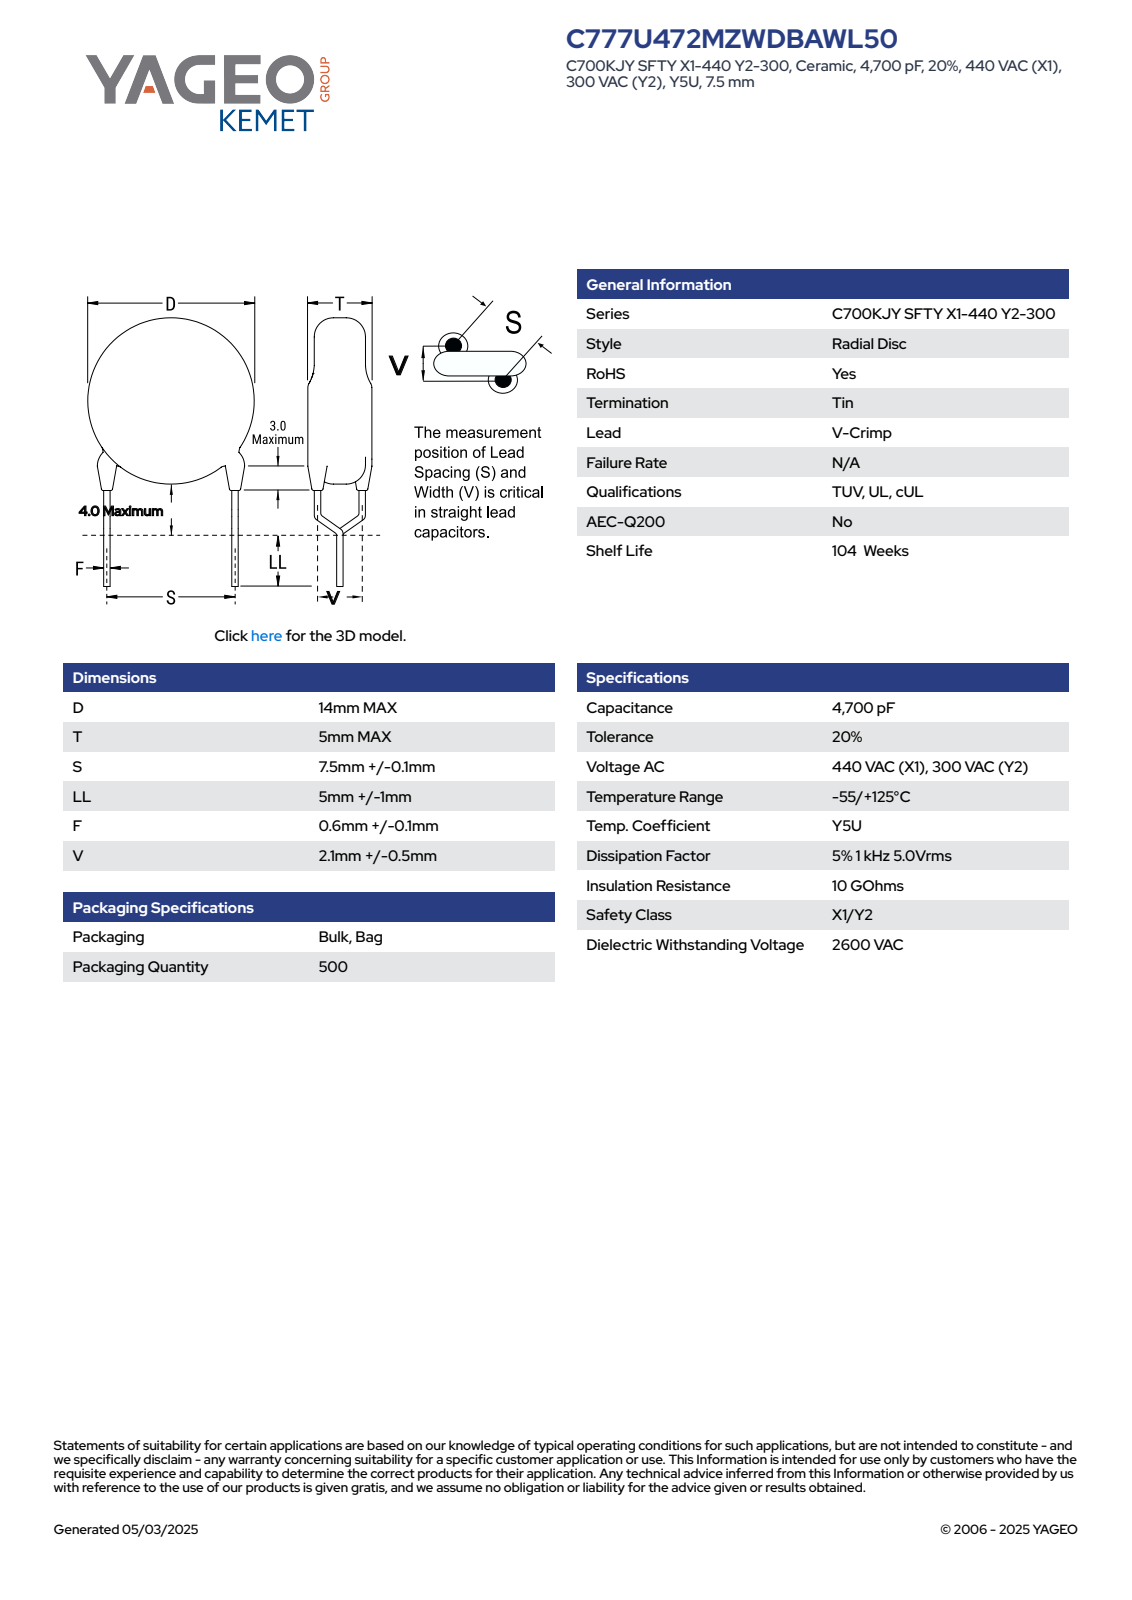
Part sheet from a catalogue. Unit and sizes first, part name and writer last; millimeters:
Units: millimetres
Overall size (bounding box): 20 × 14 × 5
Round bosses / shafts (diameter × count): ⌀0.7 ×6, ⌀1.2 ×2, ⌀14 ×1
Main face-to-face distances: 5, 6, 14.35, 8.35, 12.41, 6.41, 1.94, 0.53, 7.93, 0.37
Volume: 759 mm³ · Surface area: 548 mm²
Bodies: 4 solids, 85 faces (63 planar, 18 cylindrical, 4 other)
Part name (STEP PRODUCT): CCD_VC14X5_D14T5S7.5LL6F0.7V2.1
STEP written by: SolidWorks 2021 (AUTOMOTIVE_DESIGN)
